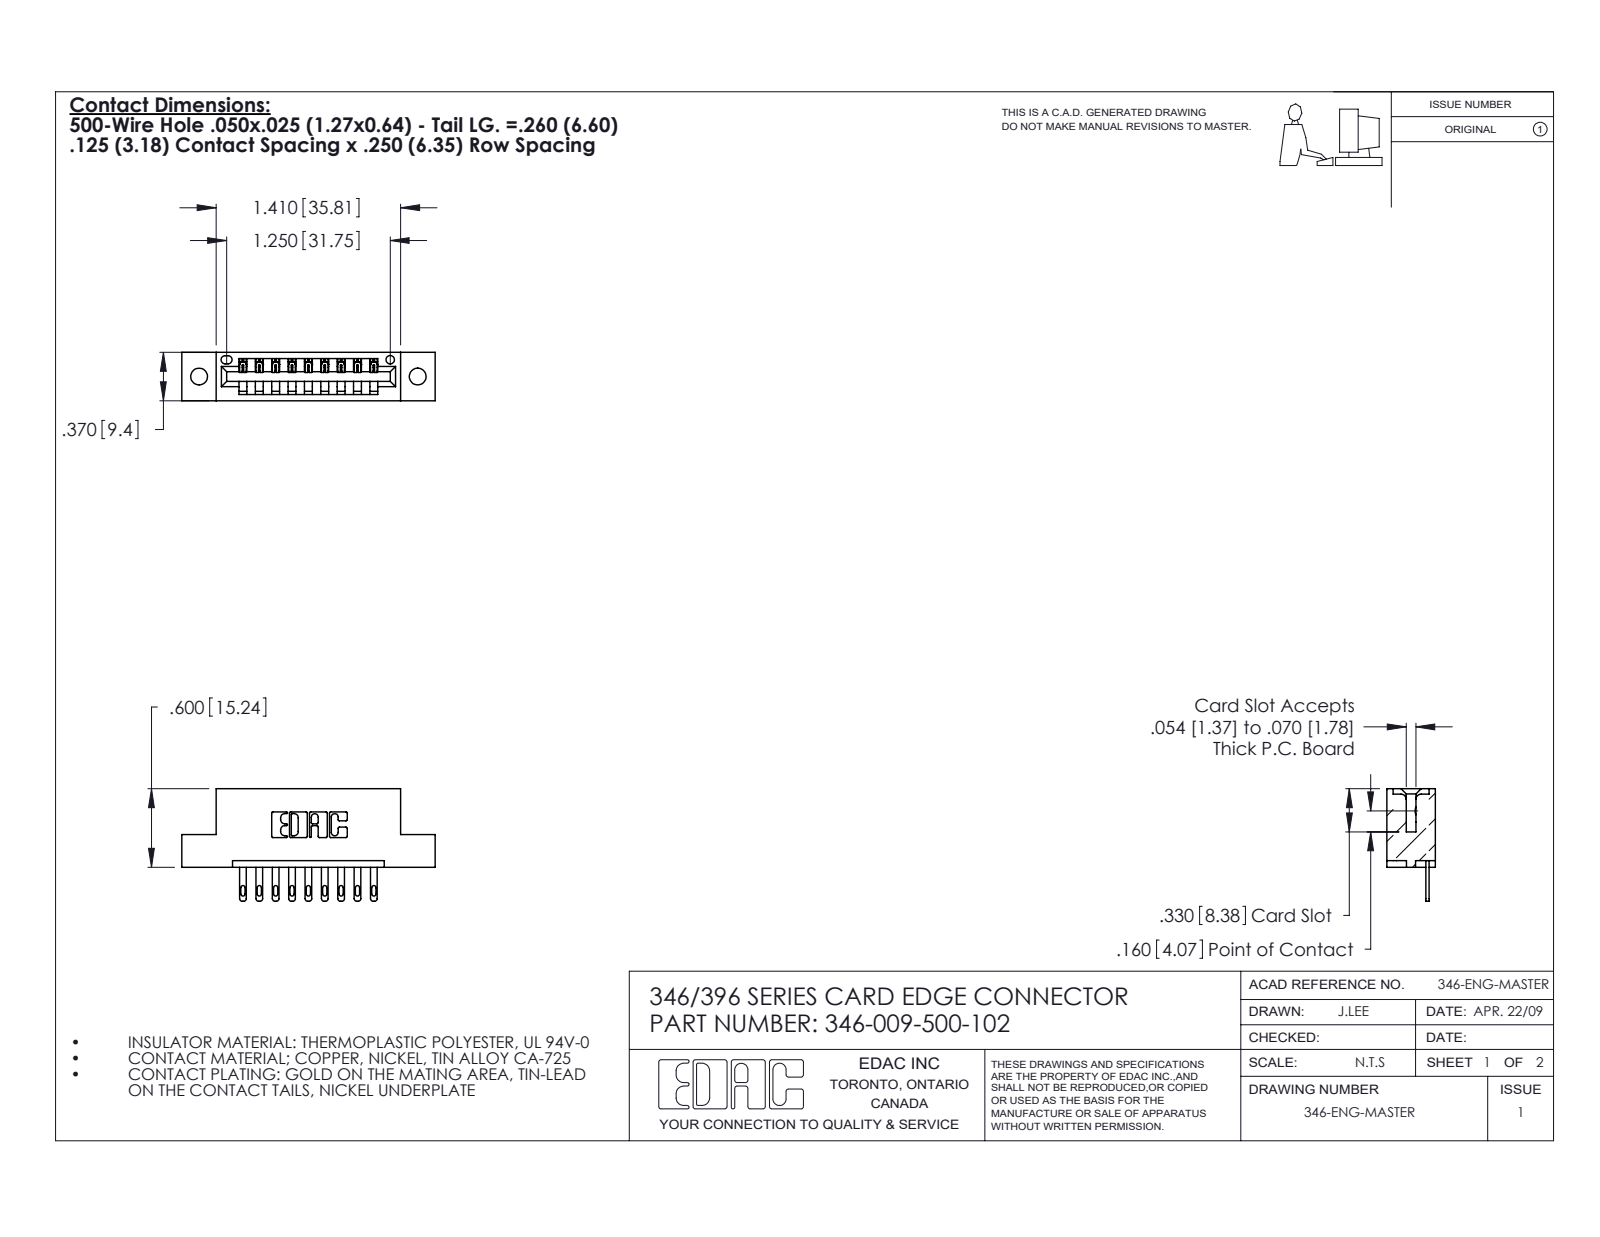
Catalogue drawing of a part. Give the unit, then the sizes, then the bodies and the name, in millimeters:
Units: millimetres
Overall size (bounding box): 49.1 × 21.8 × 9.4
Round holes (diameter × count): ⌀3.3 ×2, ⌀1.6 ×1
Partial cylindrical surfaces — rounded edges, fillets, slot ends (radius × count): R0.3 ×22, R0.2 ×18, R0.4 ×18, R0.5 ×18, R0.2 ×6, R0.8 ×6, R0.7 ×3, R0.8 ×2
Main face-to-face distances: 6.4, 1.2, 8.2, 9.4, 1.8, 7.6, 0.6, 3.8, 5.6, 2.5
Hole centre spacings: 6.2, 37.2, 42.4
Volume: 4 440 mm³ · Surface area: 4 951 mm²
Bodies: 10 solids, 608 faces (382 planar, 226 cylindrical, 0 other)
Part name (STEP PRODUCT): 345-292-001_345-293-100; 346-009-500-102; 346 Part_Flush Mounting Lugs - 0.128 Dia
STEP written by: SolidWorks 2020 (CONFIG_CONTROL_DESIGN)
